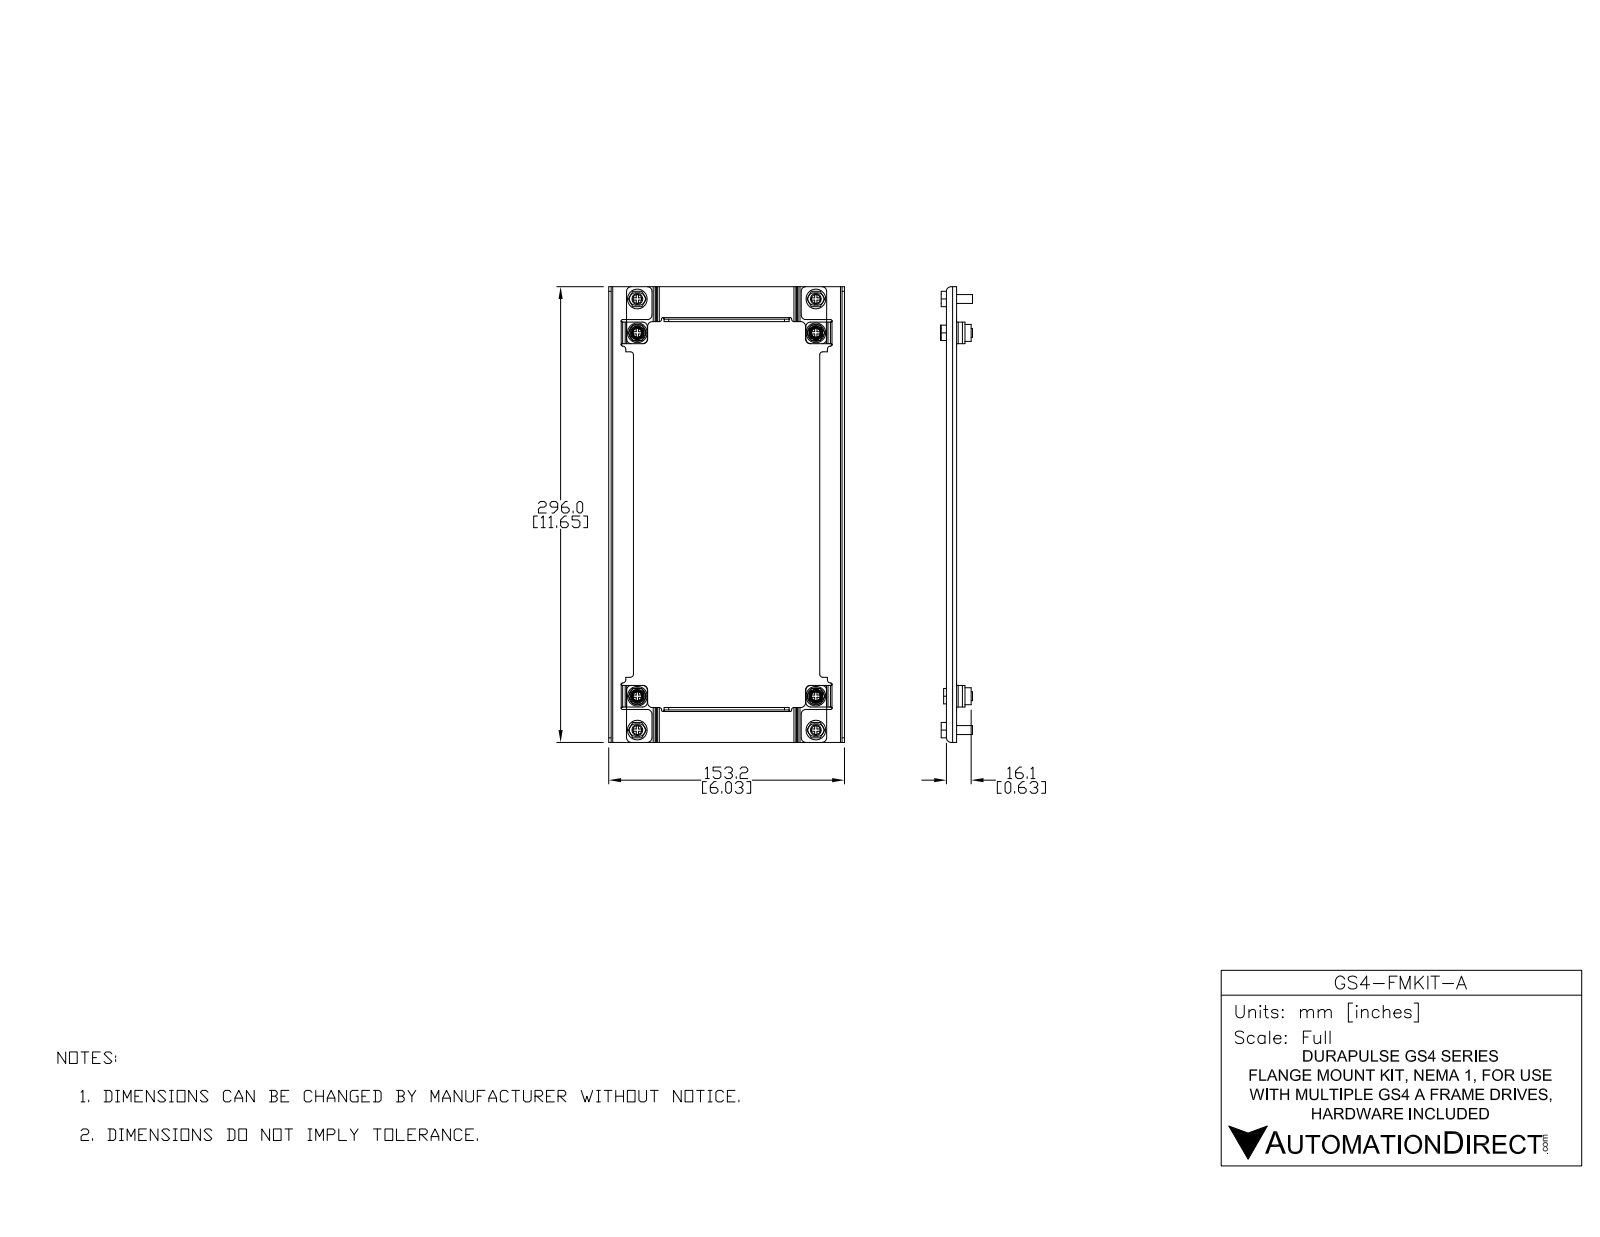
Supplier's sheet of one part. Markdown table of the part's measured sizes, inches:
| quantity | value |
| --- | --- |
| part name | GS4-FMKIT-A |
| STEP written by | SolidWorks 2015 (AUTOMOTIVE_DESIGN) |
| units | inches |
| bodies | 0 solids, 354 faces (186 planar, 140 cylindrical, 28 other) |
| overall size | 11.654 × 6.031 × 0.882 |
| round holes (diameter × count) | 0.504 × 2 |
| round bosses / shafts (diameter × count) | 0.228 × 8, 0.504 × 6, 0.435 × 4 |
| partial cylindrical surfaces (radius × count) | 0.118 × 36, 0.079 × 12, 0.039 × 8, 0.102 × 8, 0.157 × 8, 0.063 × 4, 0.142 × 4 |
| main face-to-face distances | 0.063, 5.969, 0.126, 0.134, 0.394, 5.906, 6.031, 0.26, 0.197, 0.213 |
| hole center spacings | 4.567 |
